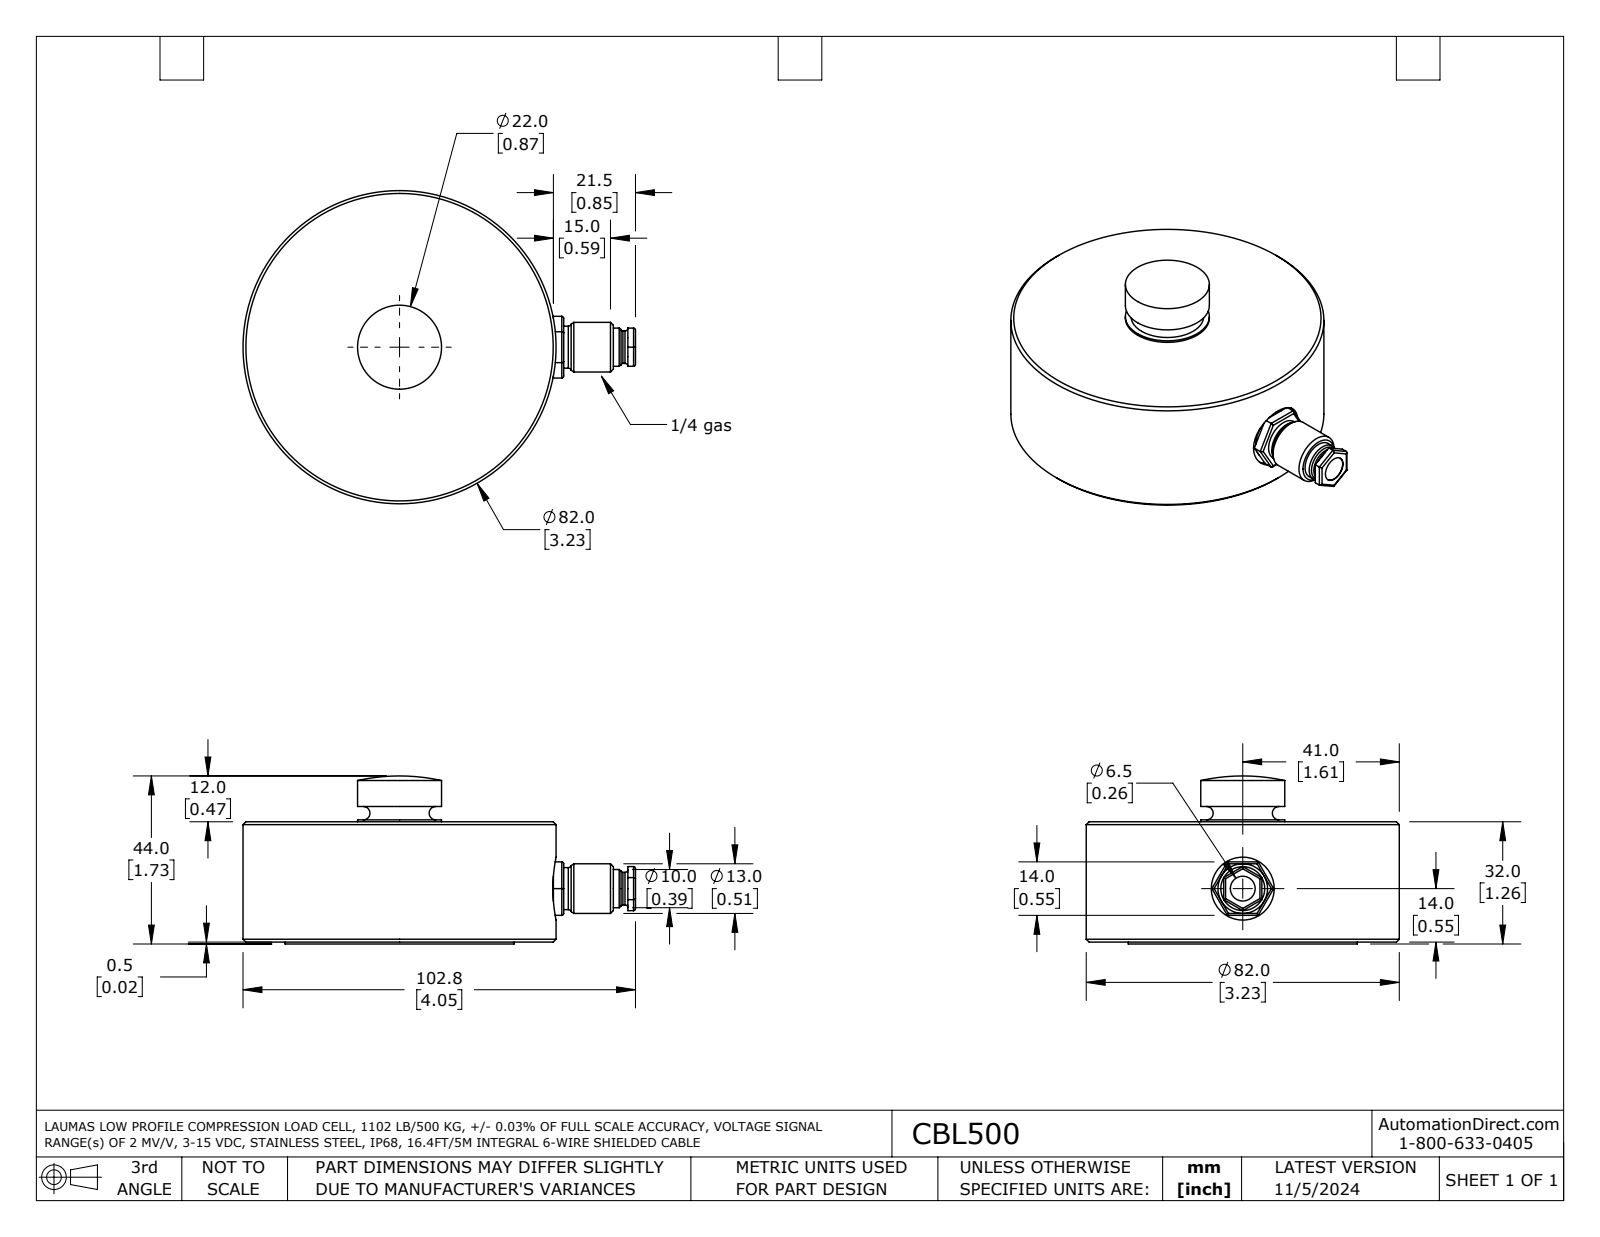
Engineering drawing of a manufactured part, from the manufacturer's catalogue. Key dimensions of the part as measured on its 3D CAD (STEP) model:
Part name (STEP PRODUCT): CBL500
STEP written by: SolidWorks 2021 (AUTOMOTIVE_DESIGN)
Units: inches
Bodies: 2 solids, 86 faces (31 planar, 36 cylindrical, 19 other)
Overall size (bounding box): 4.047 × 3.228 × 1.732
Volume: 10.42 in³ · Surface area: 32.65 in²
Round holes (diameter × count): ⌀0.256 ×1, ⌀0.65 ×1, ⌀2.15 ×1
Round bosses / shafts (diameter × count): ⌀3.228 ×1, ⌀2.362 ×1, ⌀0.866 ×1, ⌀0.531 ×1, ⌀0.512 ×1, ⌀0.433 ×1, ⌀0.394 ×1, ⌀0.335 ×1
Partial cylindrical surfaces — rounded edges, fillets, slot ends (radius × count): R0.02 ×12
Main face-to-face distances: 1.211, 0.03, 1.24, 0.02, 1.26, 0.049, 0.138, 1.28, 1.23, 1.417
